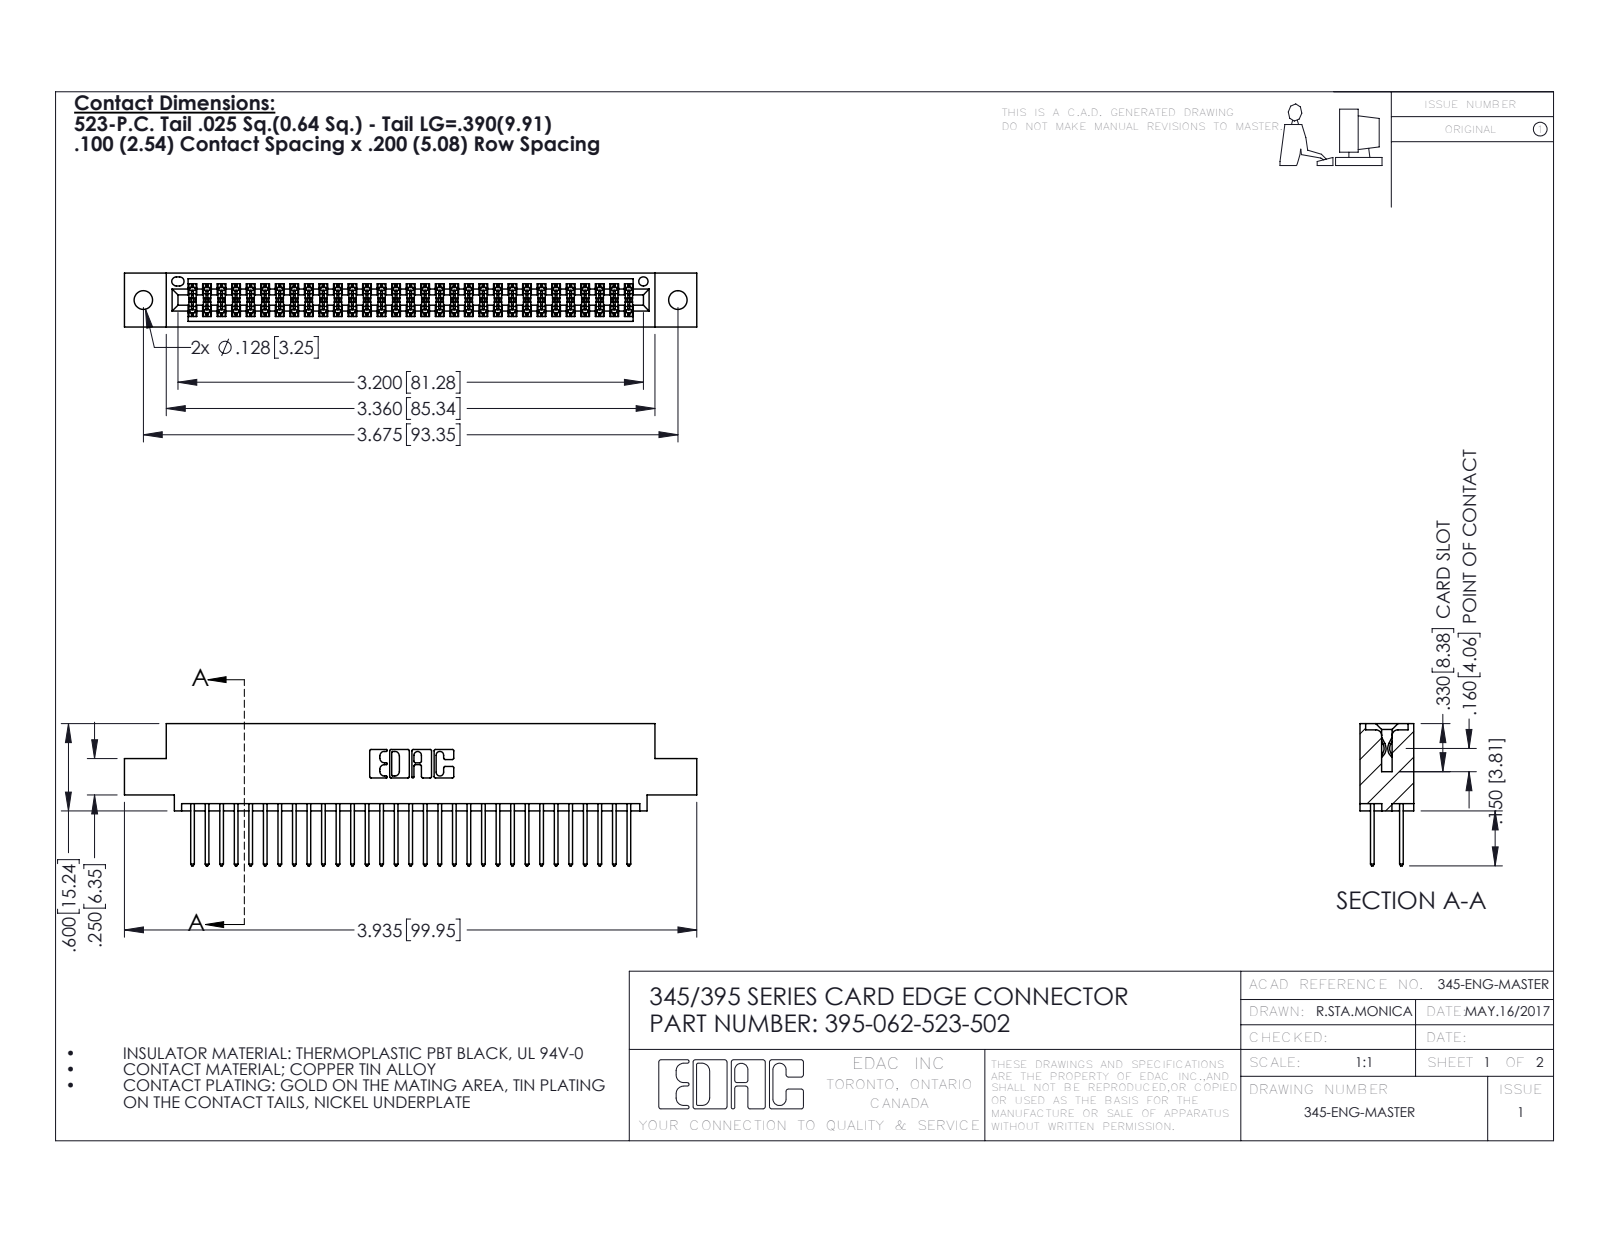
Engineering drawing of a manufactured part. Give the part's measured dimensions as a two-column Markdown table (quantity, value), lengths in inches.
| quantity | value |
| --- | --- |
| part name | 345 Part_0.110 Offset - 0.128 Dia; 345-292-001_345-293-123; 395-062-523-502 |
| STEP written by | SolidWorks 2016 (CONFIG_CONTROL_DESIGN) |
| units | inches |
| bodies | 63 solids, 3230 faces (2130 planar, 1100 cylindrical, 0 other) |
| overall size | 3.935 × 0.977 × 0.37 |
| volume | 0.587 in³ |
| surface area | 22.32 in² |
| round holes (diameter × count) | 0.128 × 2, 0.064 × 1 |
| partial cylindrical surfaces (radius × count) | 0.006 × 93, 0.01 × 62, 0.01 × 22, 0.007 × 6, 0.031 × 6, 0.026 × 3, 0.014 × 2, 0.019 × 2 |
| main face-to-face distances | 0.298, 0.072, 0.2, 0.098, 0.272, 0.025, 0.37, 0.225, 0.175, 0.149 |
| hole center spacings | 0.27, 3.44, 3.675 |
